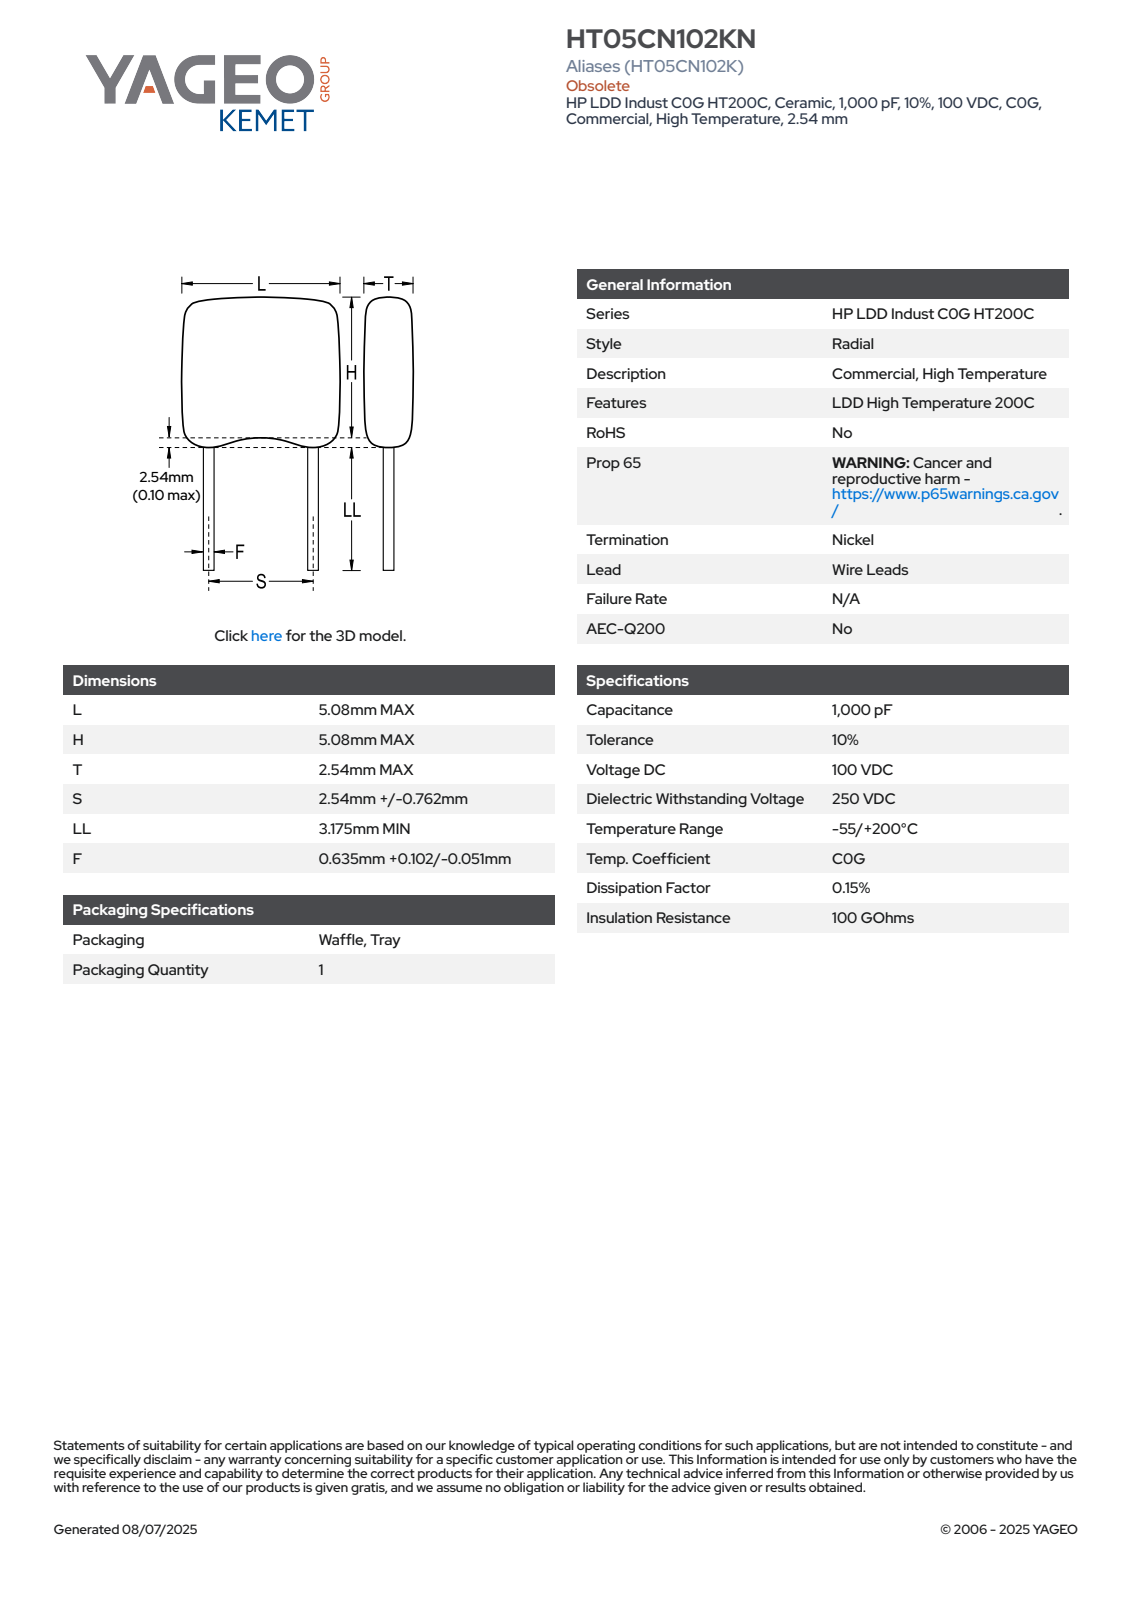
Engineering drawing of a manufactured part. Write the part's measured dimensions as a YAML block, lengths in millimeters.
part_name: "CCR_RCST2_HT05_L5.08H5.08T2.54S2.54LL3.175F0.737"
step_written_by: "SolidWorks 2021 (AUTOMOTIVE_DESIGN)"
units: millimeters
bodies: {solids: 4, faces: 98, planar: 68, cylindrical: 18, other: 12}
overall_size: [10.79, 5.08, 2.54]
volume: 85
surface_area: 141
round_bosses_or_shafts:
  - {diameter: 0.74, count: 2}
partial_cylinders:
  - {radius: 1, count: 10}
face_to_face_distances: [2.54, 5.08, 10.79, 3.17, 7.62, 7.97, 4.8, 2.82, 7.28, 4.11]
